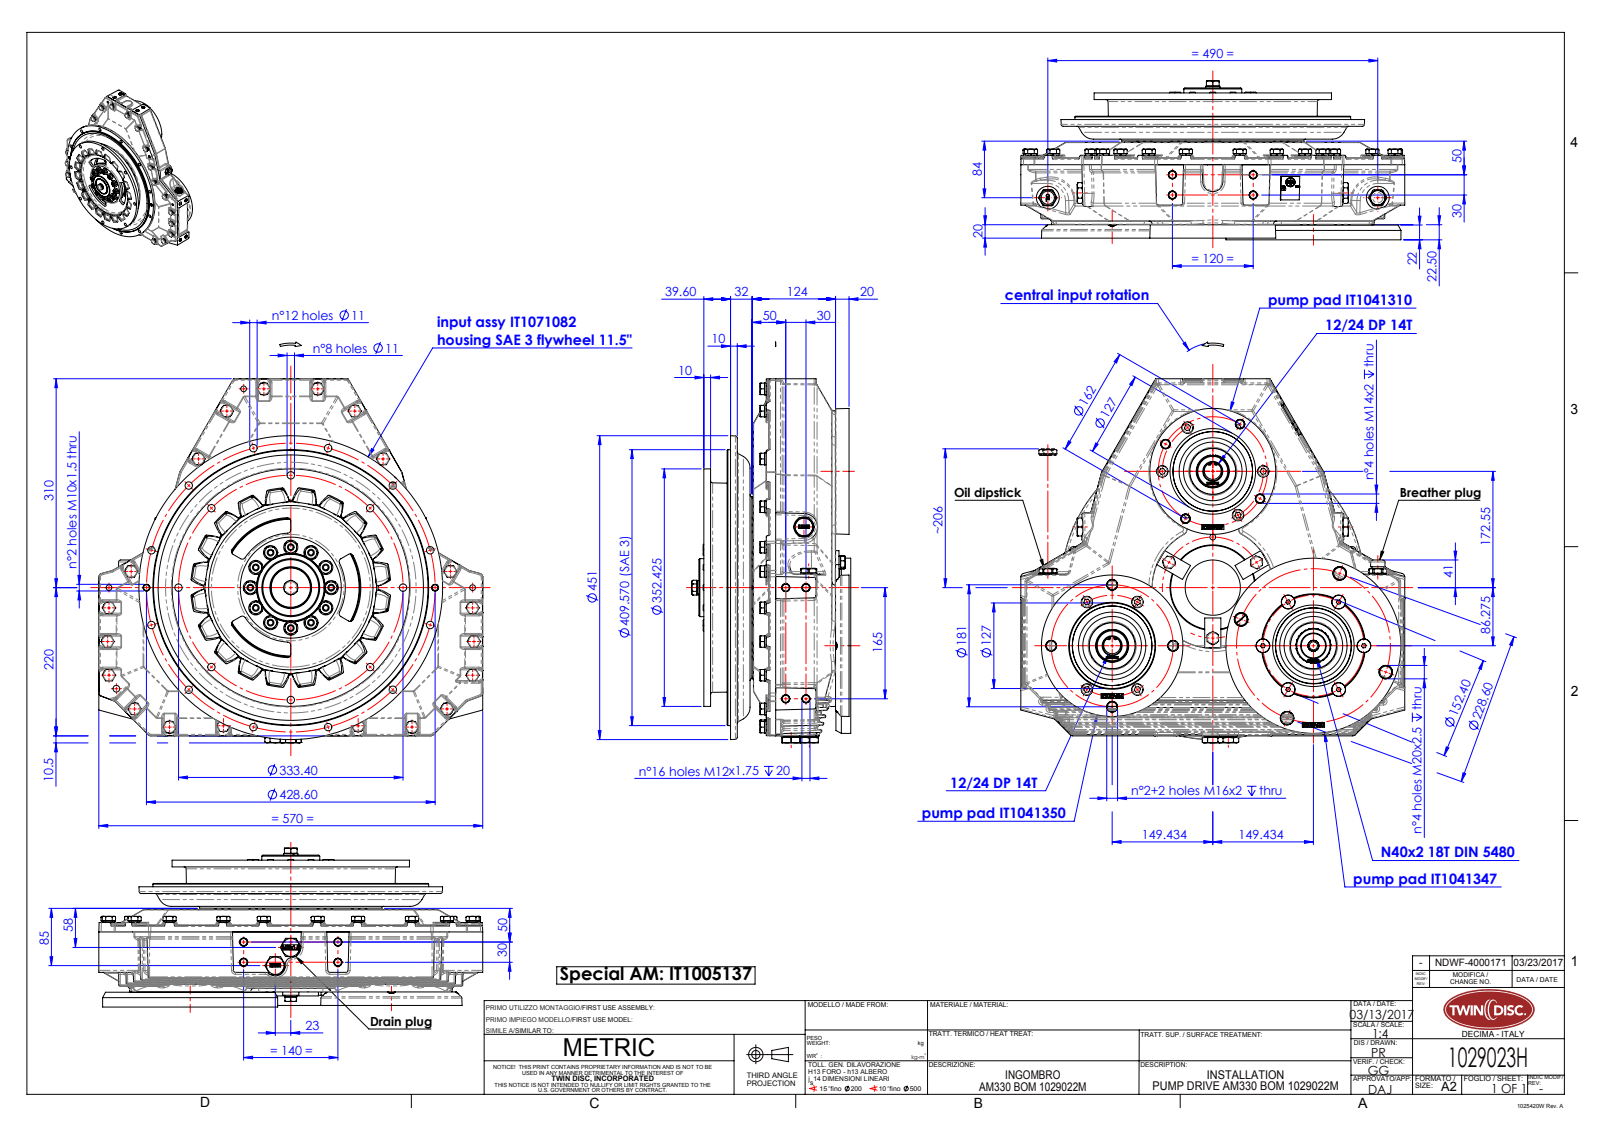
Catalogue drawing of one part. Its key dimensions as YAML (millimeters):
part_name: "IT1041350_rev00-installation; IT1071082_rev02-installation; 1029023H; IT4588040_rev00-installation (+7 more)"
step_written_by: "SolidWorks 2015 (AUTOMOTIVE_DESIGN)"
units: millimeters
bodies: {solids: 39, faces: 8201, planar: 3484, cylindrical: 2237, other: 2480}
overall_size: [595.04, 570, 236]
volume: 7049000
surface_area: 3218000
round_holes:
  - {diameter: 10.2, count: 48}
  - {diameter: 10.5, count: 38}
  - {diameter: 8.5, count: 35}
  - {diameter: 11, count: 29}
  - {diameter: 12, count: 16}
  - {diameter: 10, count: 11}
  - {diameter: 14, count: 8}
  - {diameter: 17, count: 8}
  - {diameter: 12.2, count: 7}
  - {diameter: 13, count: 7}
  - {diameter: 20, count: 6}
  - {diameter: 20.5, count: 6}
round_bosses_or_shafts:
  - {diameter: 10, count: 55}
  - {diameter: 16.2, count: 41}
  - {diameter: 18.1, count: 29}
  - {diameter: 21, count: 12}
  - {diameter: 16, count: 9}
  - {diameter: 21.1, count: 7}
  - {diameter: 20, count: 7}
  - {diameter: 18, count: 7}
partial_cylinders:
  - {radius: 2, count: 343}
  - {radius: 3, count: 163}
  - {radius: 5, count: 86}
  - {radius: 1, count: 80}
  - {radius: 4, count: 80}
  - {radius: 0.25, count: 50}
  - {radius: 2.5, count: 40}
  - {radius: 42.91, count: 40}
face_to_face_distances: [10, 89, 2, 11.5, 15, 33, 17, 21.5, 110.5, 24]
hole_center_spacings: [120, 75, 30, 57.4, 91.16, 106.07, 138.58, 10]
